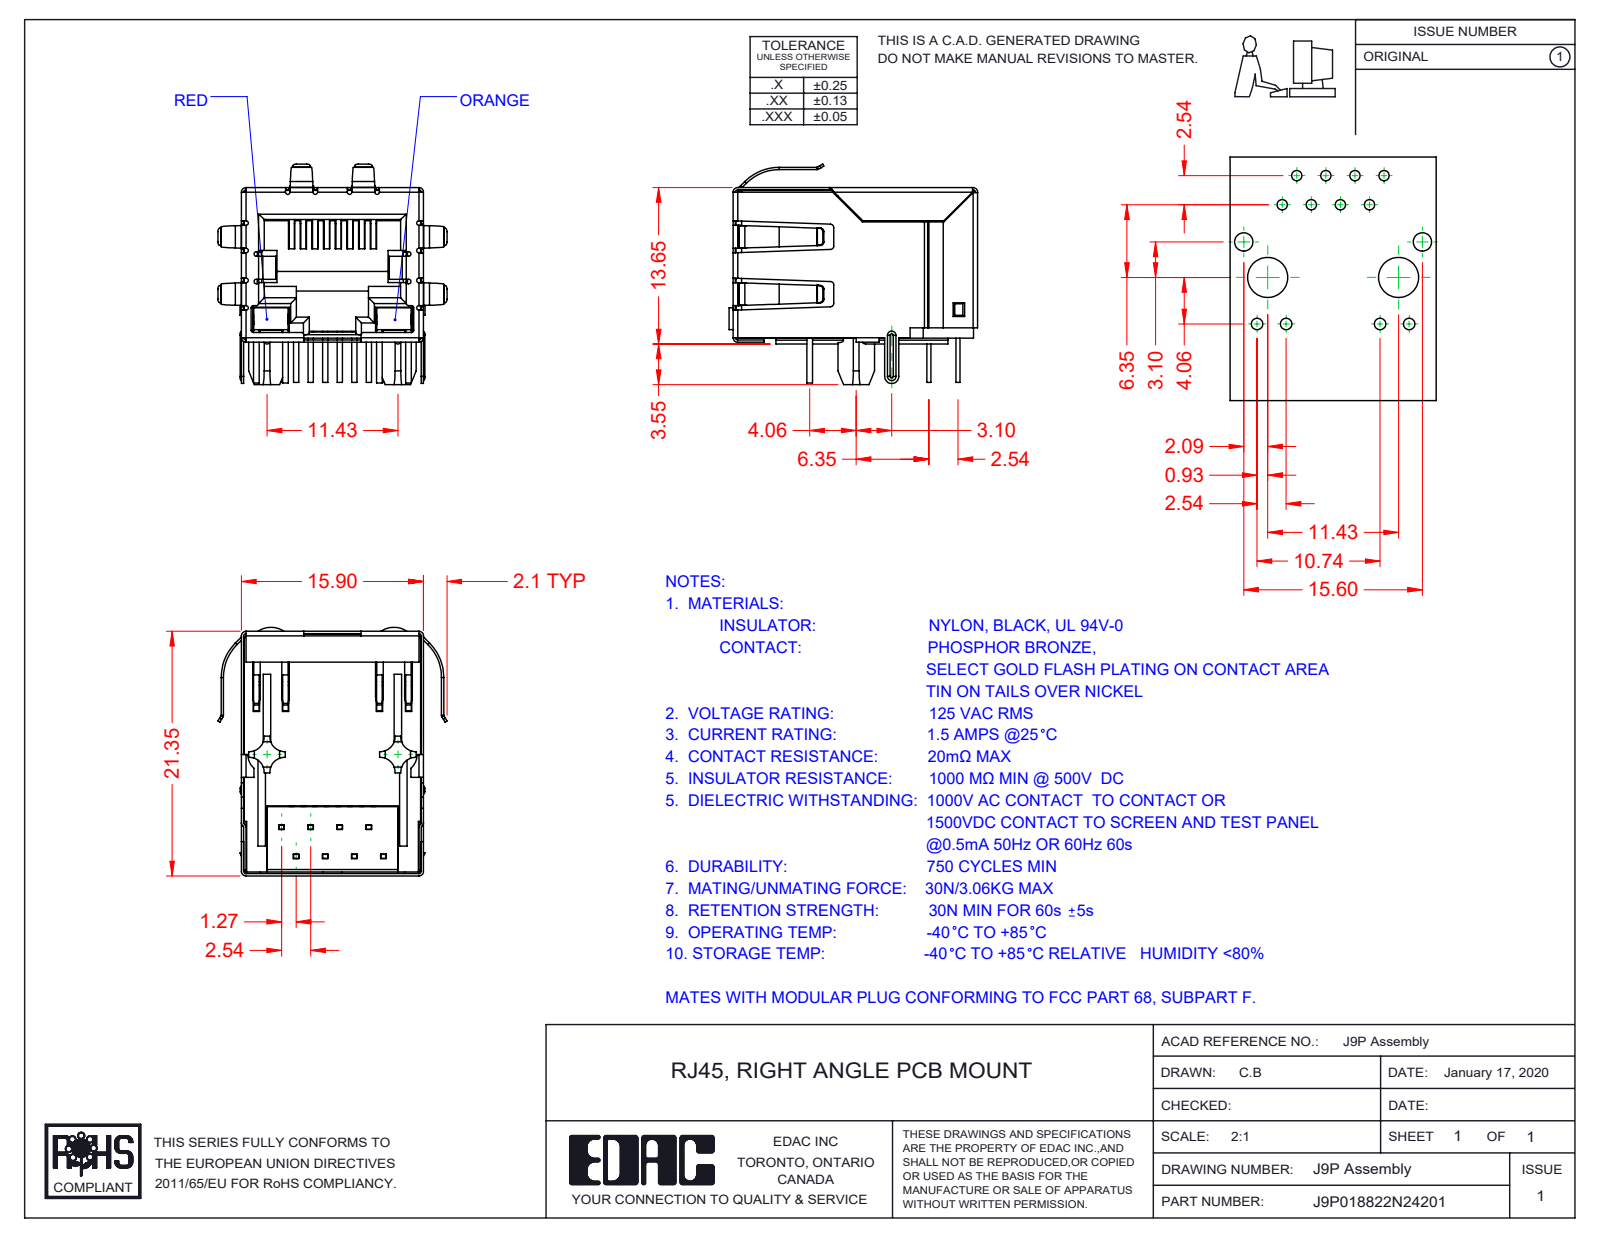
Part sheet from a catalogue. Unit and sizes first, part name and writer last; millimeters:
Units: millimetres
Overall size (bounding box): 21.7 × 20 × 19.25
Partial cylindrical surfaces — rounded edges, fillets, slot ends (radius × count): R0.2 ×39, R0.5 ×22, R0.3 ×20, R0.4 ×16, R1.3 ×8, R0.23 ×5, R0.11 ×4, R0.31 ×4
Main face-to-face distances: 15.45, 15.7, 15.65, 0.35, 0.54, 15.5, 12.36, 0.6, 1.4, 0.59
Volume: 2 687 mm³ · Surface area: 7 515 mm²
Bodies: 13 solids, 1472 faces (1042 planar, 336 cylindrical, 94 other)
Part name (STEP PRODUCT): 9P-LED Contact Lock; 9P-LED Contacts; 9P-LED Insulator; 9P-LED LED RH_4-Orange (+4 more)
STEP written by: SolidWorks 2016 (CONFIG_CONTROL_DESIGN)
